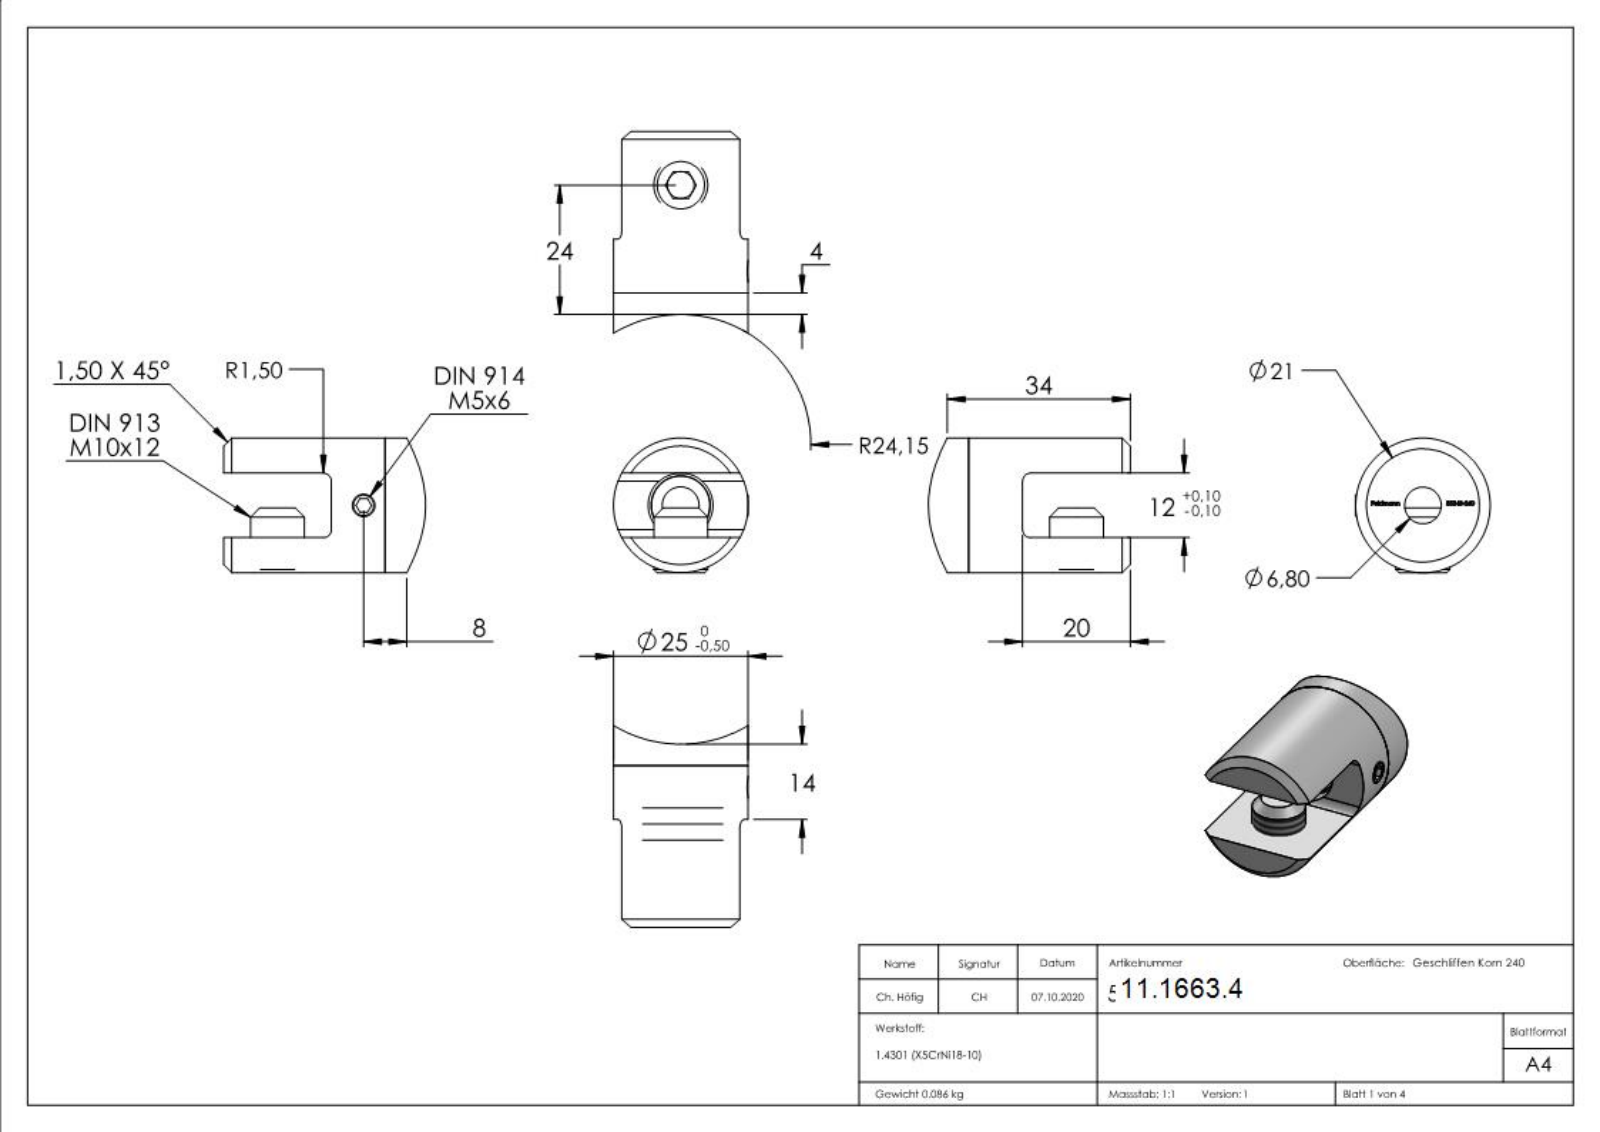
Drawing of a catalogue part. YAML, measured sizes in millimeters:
part_name: "5534X-240 Teil1; 55343-240; DIN913; DIN914 (+5 more)"
step_written_by: "SolidWorks 2018 (CONFIG_CONTROL_DESIGN)"
units: millimeters
bodies: {solids: 4, faces: 588, planar: 312, cylindrical: 28, other: 248}
overall_size: [70, 70, 37.49]
volume: 10054
surface_area: 6667
round_holes:
  - {diameter: 4.2, count: 1}
  - {diameter: 6.8, count: 1}
  - {diameter: 8.5, count: 1}
  - {diameter: 21, count: 1}
round_bosses_or_shafts:
  - {diameter: 25, count: 1}
  - {diameter: 12, count: 1}
  - {diameter: 10, count: 1}
  - {diameter: 5, count: 1}
partial_cylinders:
  - {radius: 1.5, count: 2}
  - {radius: 24.15, count: 1}
face_to_face_distances: [12, 2, 32, 30, 10, 20, 6.5, 5, 18.5, 7.5]
